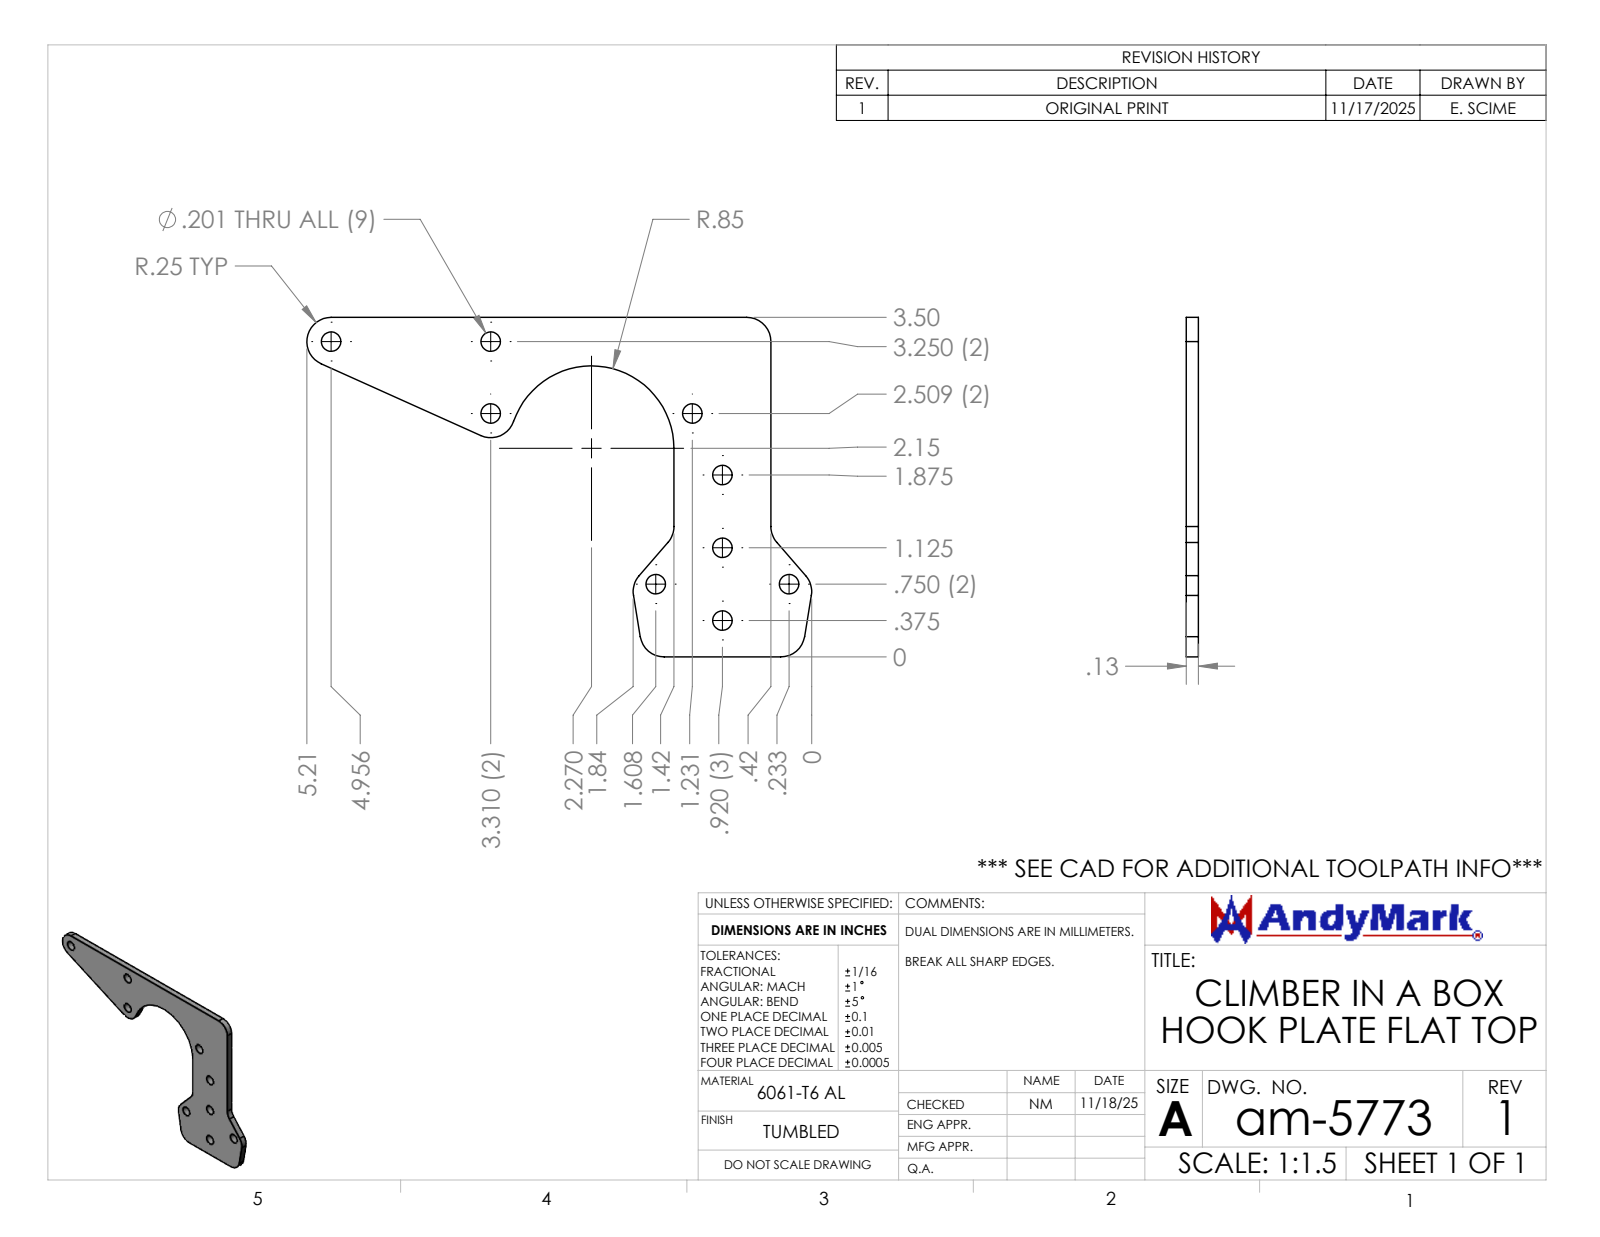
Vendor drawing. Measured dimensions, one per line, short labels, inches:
name: am-5773 Climber in a Box Hook Plate Flat Top
written by: SolidWorks 2024 (AUTOMOTIVE_DESIGN)
unit: in
bodies: 1 solid, 40 faces (11 planar, 29 cylindrical, 0 other)
size: 5.206 × 3.5 × 0.125
volume: 0.865 in³; area: 16.69 in²
holes: 9× ⌀0.201
rounds: 9× R0.25, 1× R0.85
face distances: 0.125, 3.5, 1
hole spacings: 0.783, 0.75, 1.319, 0.706, 0.741, 1.375, 1.419, 1.5
